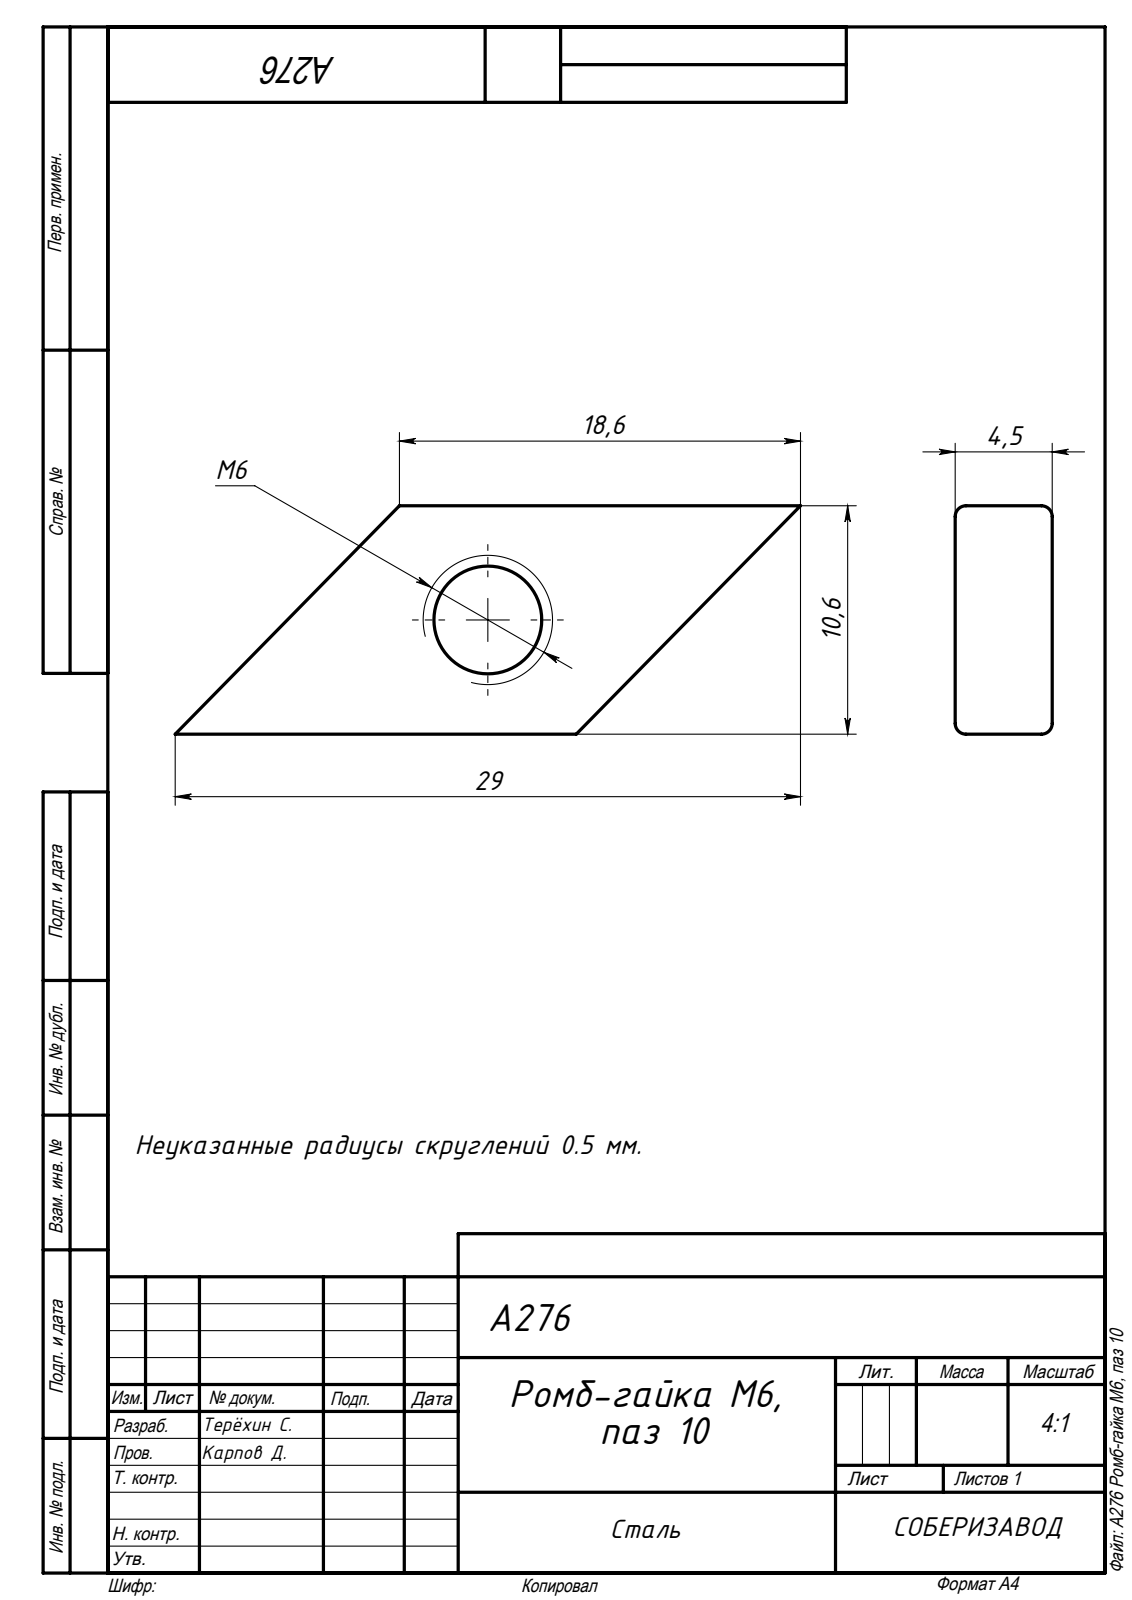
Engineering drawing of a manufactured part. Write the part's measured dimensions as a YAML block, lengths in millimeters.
part_name: "А276 Ромб-гайка М6, паз 10"
step_written_by: "SolidWorks 2020 (AUTOMOTIVE_DESIGN)"
units: millimeters
bodies: {solids: 1, faces: 16, planar: 6, cylindrical: 10, other: 0}
overall_size: [29, 10.6, 4.5]
volume: 792
surface_area: 698
round_holes:
  - {diameter: 5, count: 1}
partial_cylinders:
  - {radius: 0.5, count: 8}
face_to_face_distances: [4.5, 10.6, 13.28]
